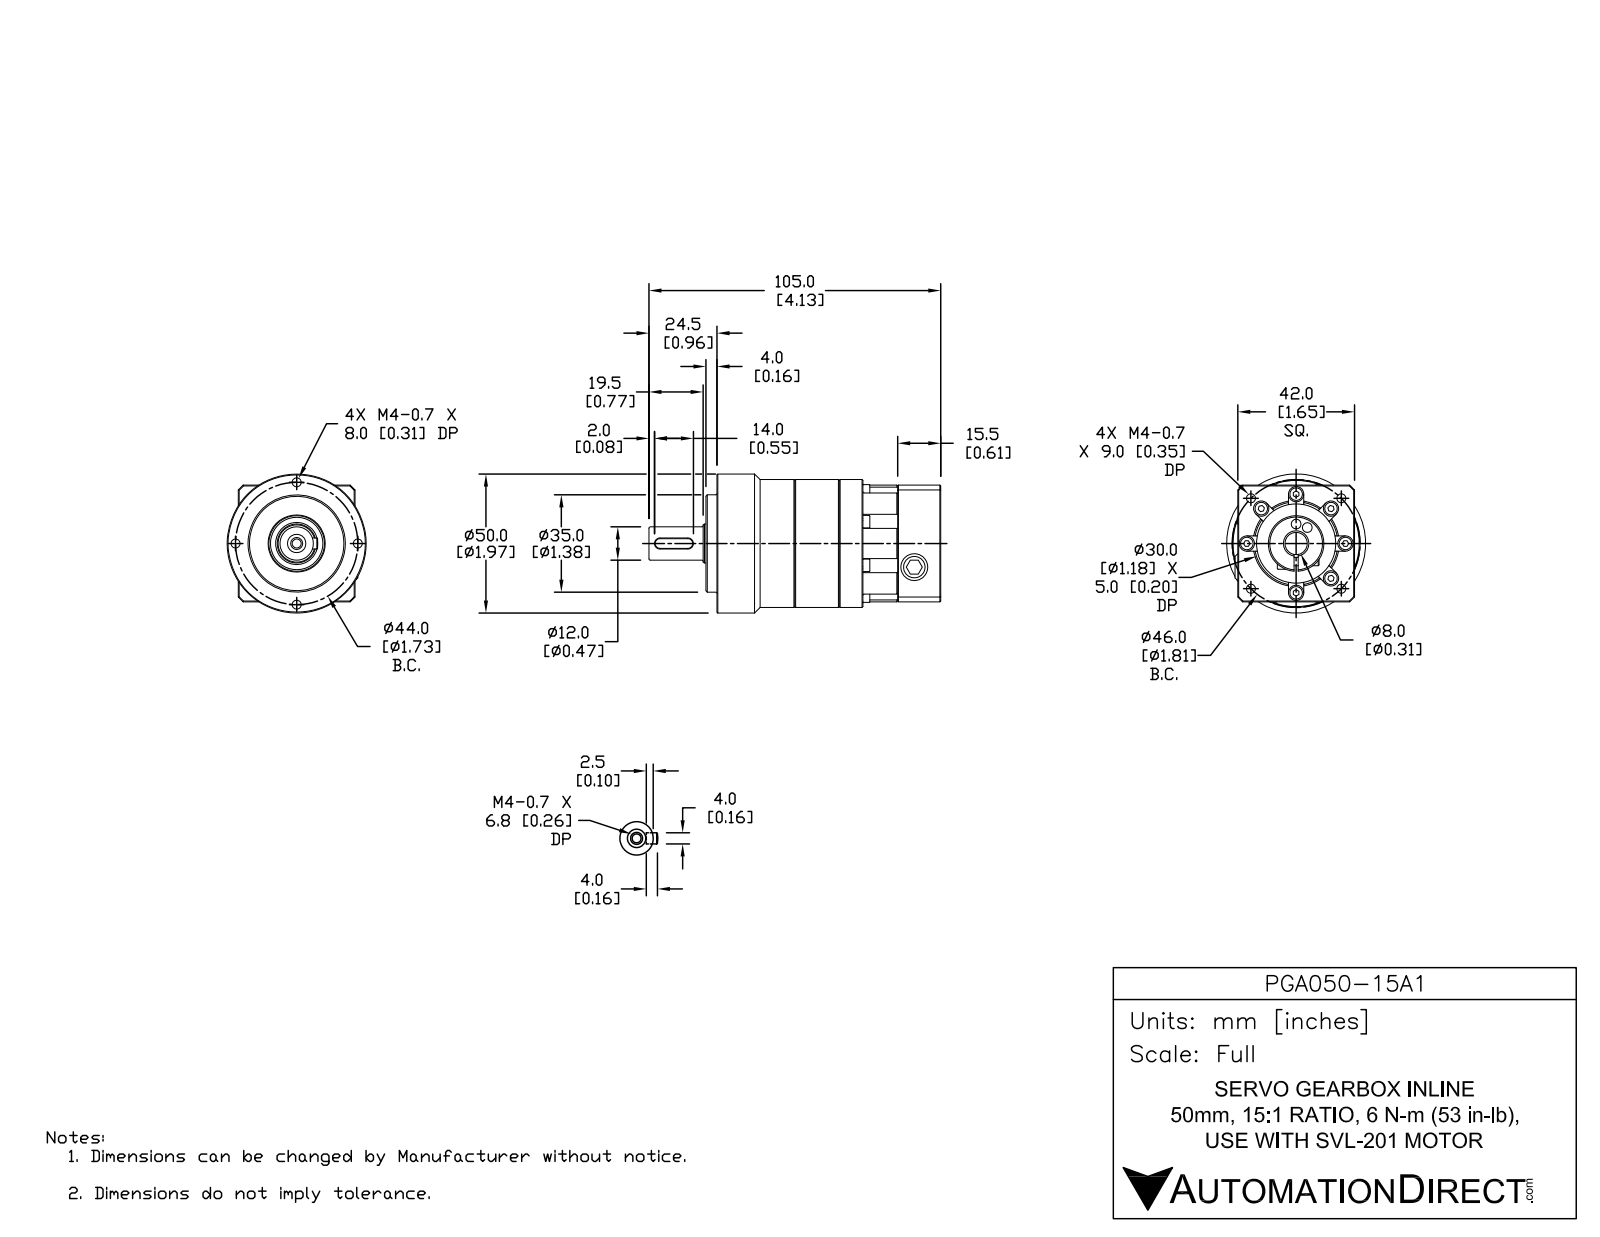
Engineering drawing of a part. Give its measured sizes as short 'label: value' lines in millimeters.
name: PGA050-15A1
written by: SolidWorks 2014 (AUTOMOTIVE_DESIGN)
unit: mm
bodies: 1 solid, 576 faces (229 planar, 161 cylindrical, 186 other)
size: 105 × 50 × 50
volume: 129 600 mm³; area: 25 020 mm²
holes: 9× ⌀3.3, 7× ⌀2.8, 7× ⌀5.5, 3× ⌀3.5, 1× ⌀4.3, 1× ⌀8, 1× ⌀20, 1× ⌀28.5
bosses: 15× ⌀4.5, 7× ⌀2.5, 1× ⌀50, 1× ⌀46, 1× ⌀35, 1× ⌀14, 1× ⌀12, 1× ⌀5.5
rounds: 8× R2.7, 2× R2, 1× R1.2, 1× R3.3, 1× R4, 1× R15, 1× R21, 1× R28.5
face distances: 42, 65, 4, 80.5, 15.5, 84.5, 69, 5, 14, 79.5
hole spacings: 16.3, 17.2, 28.3, 37.7, 41.6, 17.8, 13.6, 15.7
